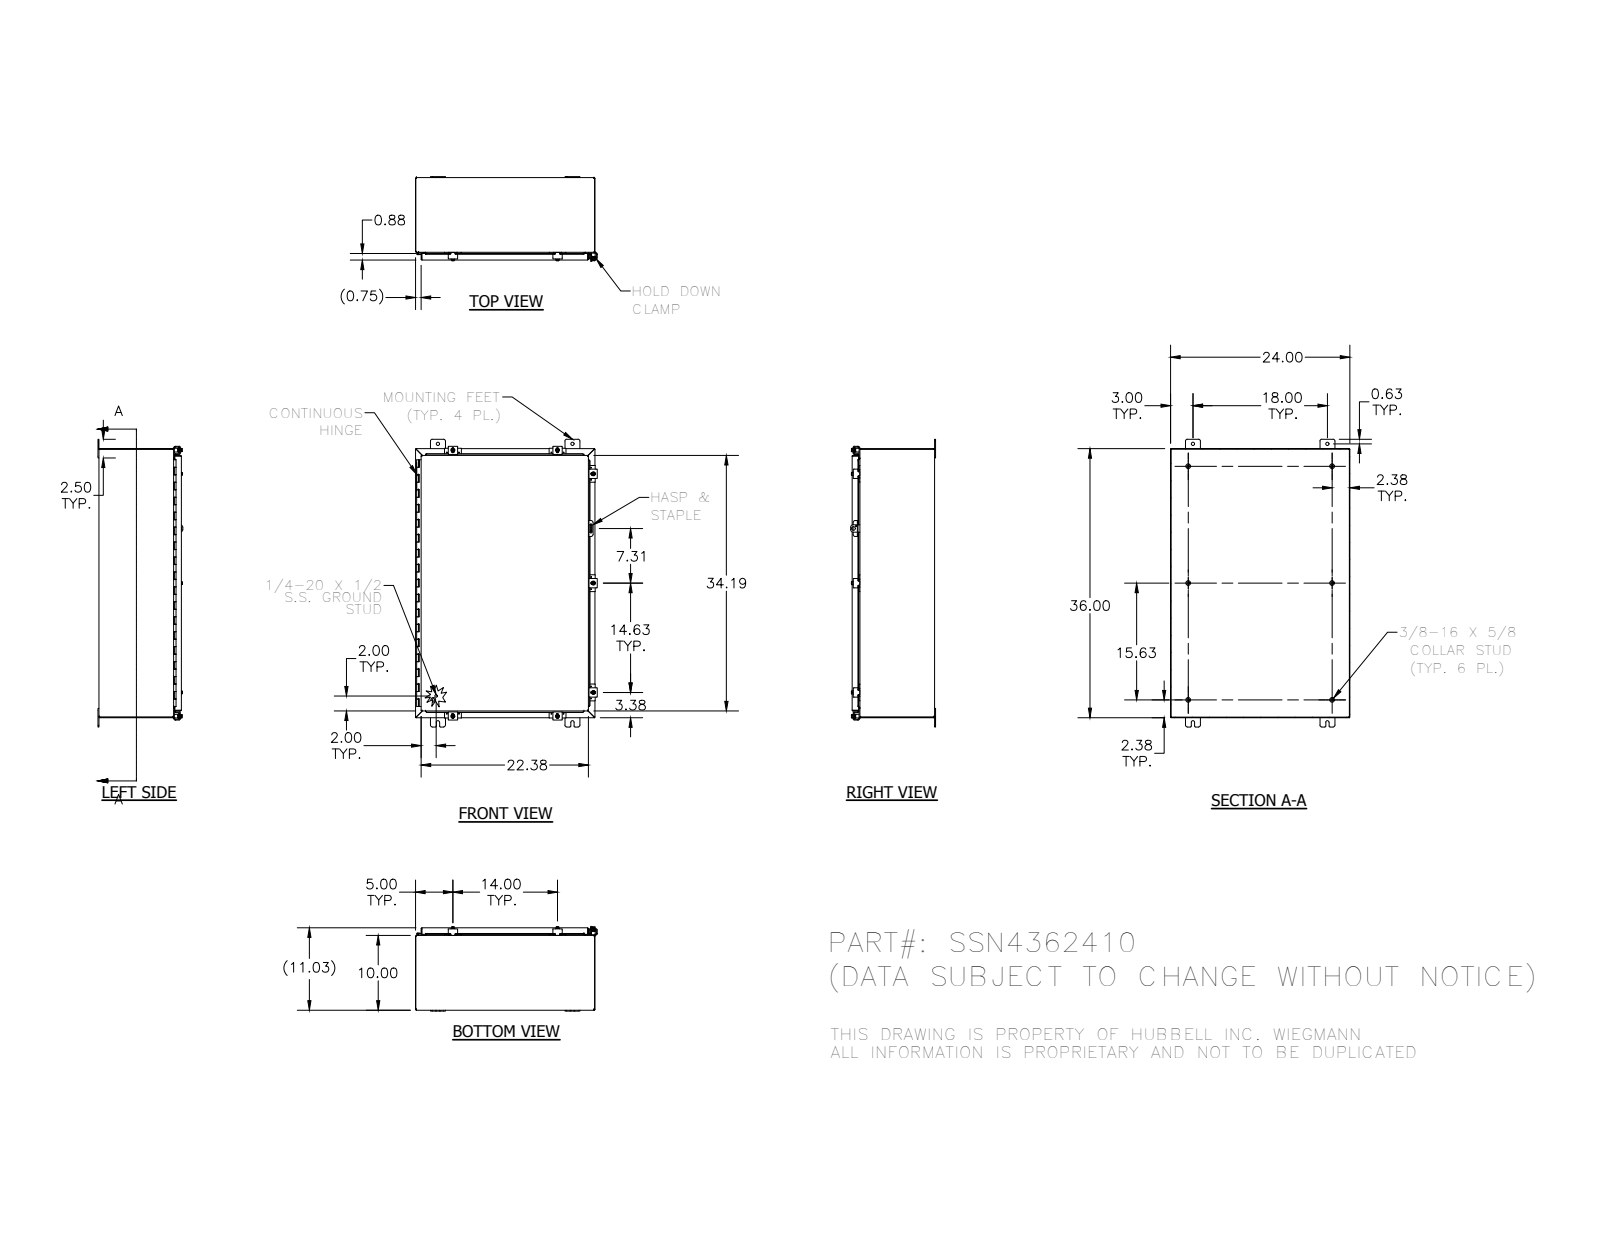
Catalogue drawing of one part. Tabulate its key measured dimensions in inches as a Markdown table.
| quantity | value |
| --- | --- |
| part name | 328140L; HFW30825-2; 38859; 328140 (+8 more) |
| STEP written by | SolidWorks 2014 (AUTOMOTIVE_DESIGN) |
| units | inches |
| bodies | 54 solids, 2204 faces (846 planar, 983 cylindrical, 375 other) |
| overall size | 38.5 × 24.311 × 11.355 |
| volume | 258.7 in³ |
| surface area | 6 823 in² |
| round holes (diameter × count) | 0.11 × 14, 0.211 × 7, 0.281 × 7, 0.3 × 7, 0.438 × 4, 0.125 × 1, 0.156 × 1, 0.5 × 1 |
| round bosses / shafts (diameter × count) | 0.25 × 9, 0.52 × 7, 0.5 × 7, 0.35 × 7, 0.625 × 6, 0.33 × 6, 0.115 × 2, 0.337 × 1 |
| partial cylindrical surfaces (radius × count) | 0.03 × 83, 0.125 × 37, 0.25 × 33, 0.031 × 23, 0.105 × 23, 0.062 × 15, 0.141 × 14, 0.1 × 10 |
| main face-to-face distances | 0.074, 10.959, 10.885, 11.033, 23.926, 35.926, 23.852, 24, 9.926, 1.033 |
| hole center spacings | 0.876, 35.298, 14, 1.625, 13.191, 14.816, 34.961, 34.998 |
